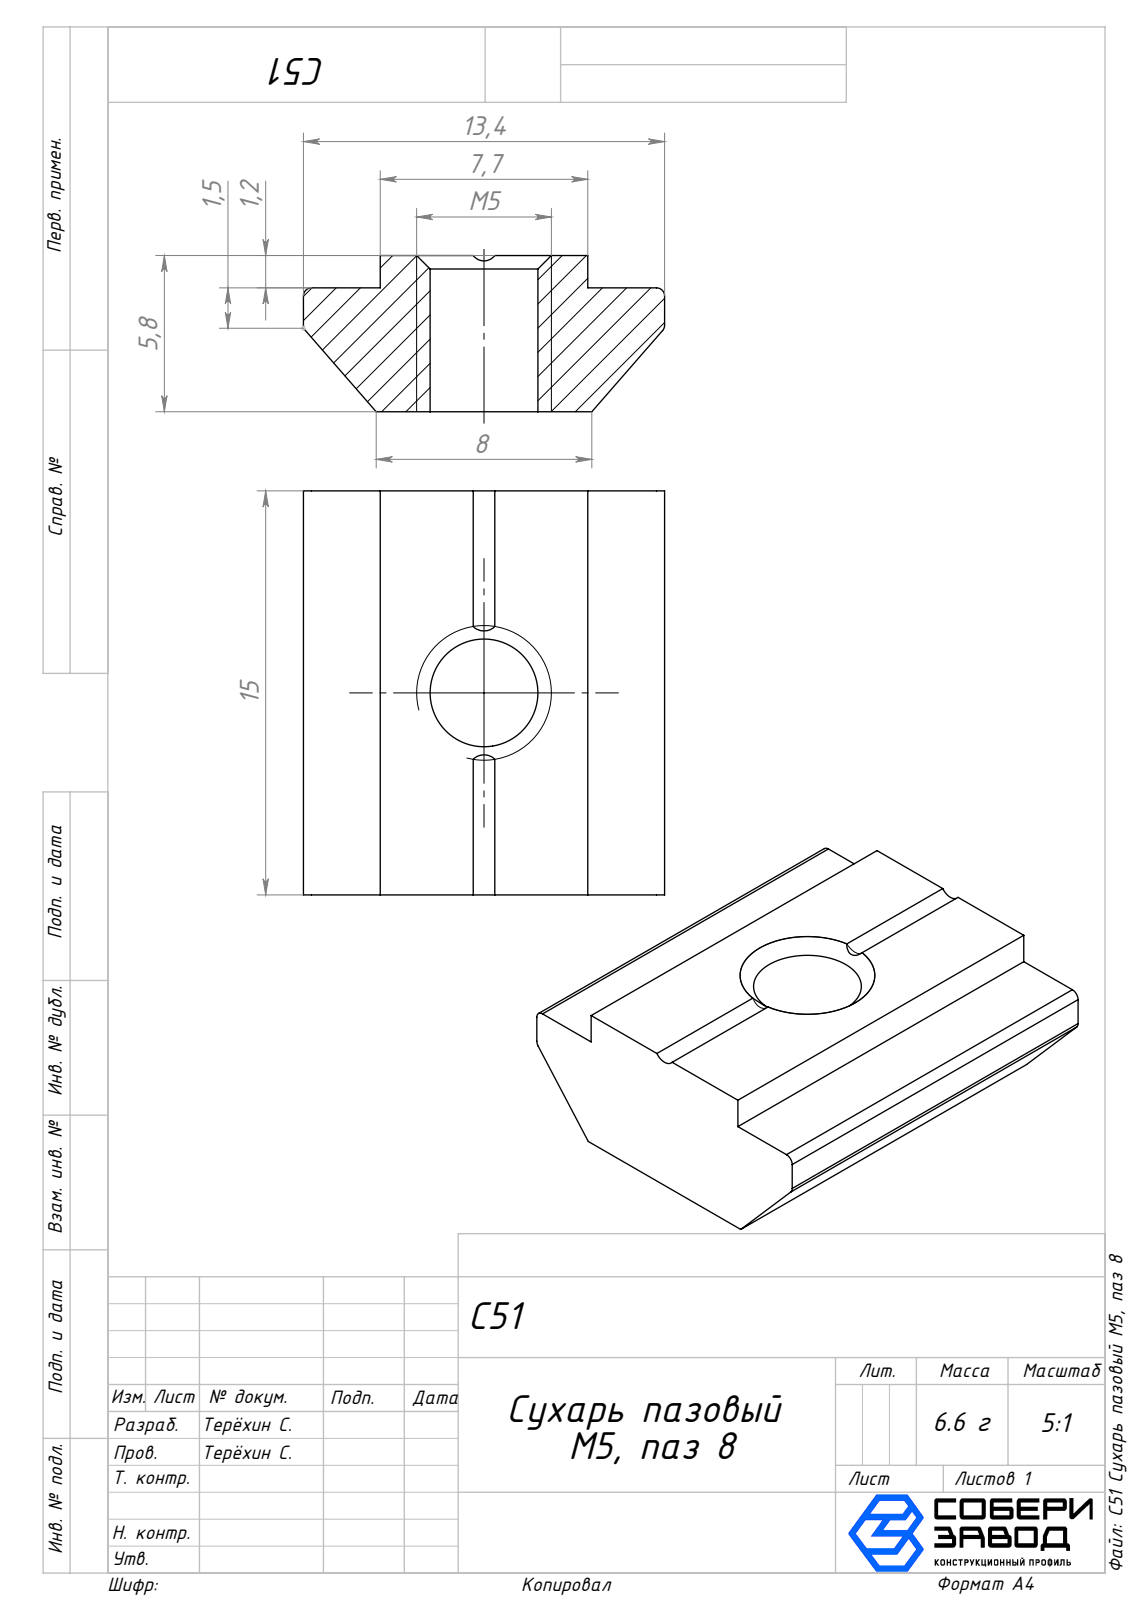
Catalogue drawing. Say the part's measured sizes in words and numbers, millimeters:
The part is named "C51 Сухарь пазовый М5, паз 8_00; Сборка1". Its 3-D file was written by "SolidWorks 2025 (AUTOMOTIVE_DESIGN)". It is 1 solid with 23 faces: 13 planar, 8 cylindrical and 2 other. Overall it measures 15 by 13.4 by 5.8 millimeters. Its volume is 861 cubic millimeters and its surface area 691 square millimeters. Round holes: 1 of diameter 4. Partial cylindrical surfaces (rounded edges, fillets, slot ends): 4 of radius 0.3, 1 of radius 0.5. The main face-to-face distances are 5.8, 4.6, 1.2, 15, 2.85, 10.55, 7.7, 13.4.
